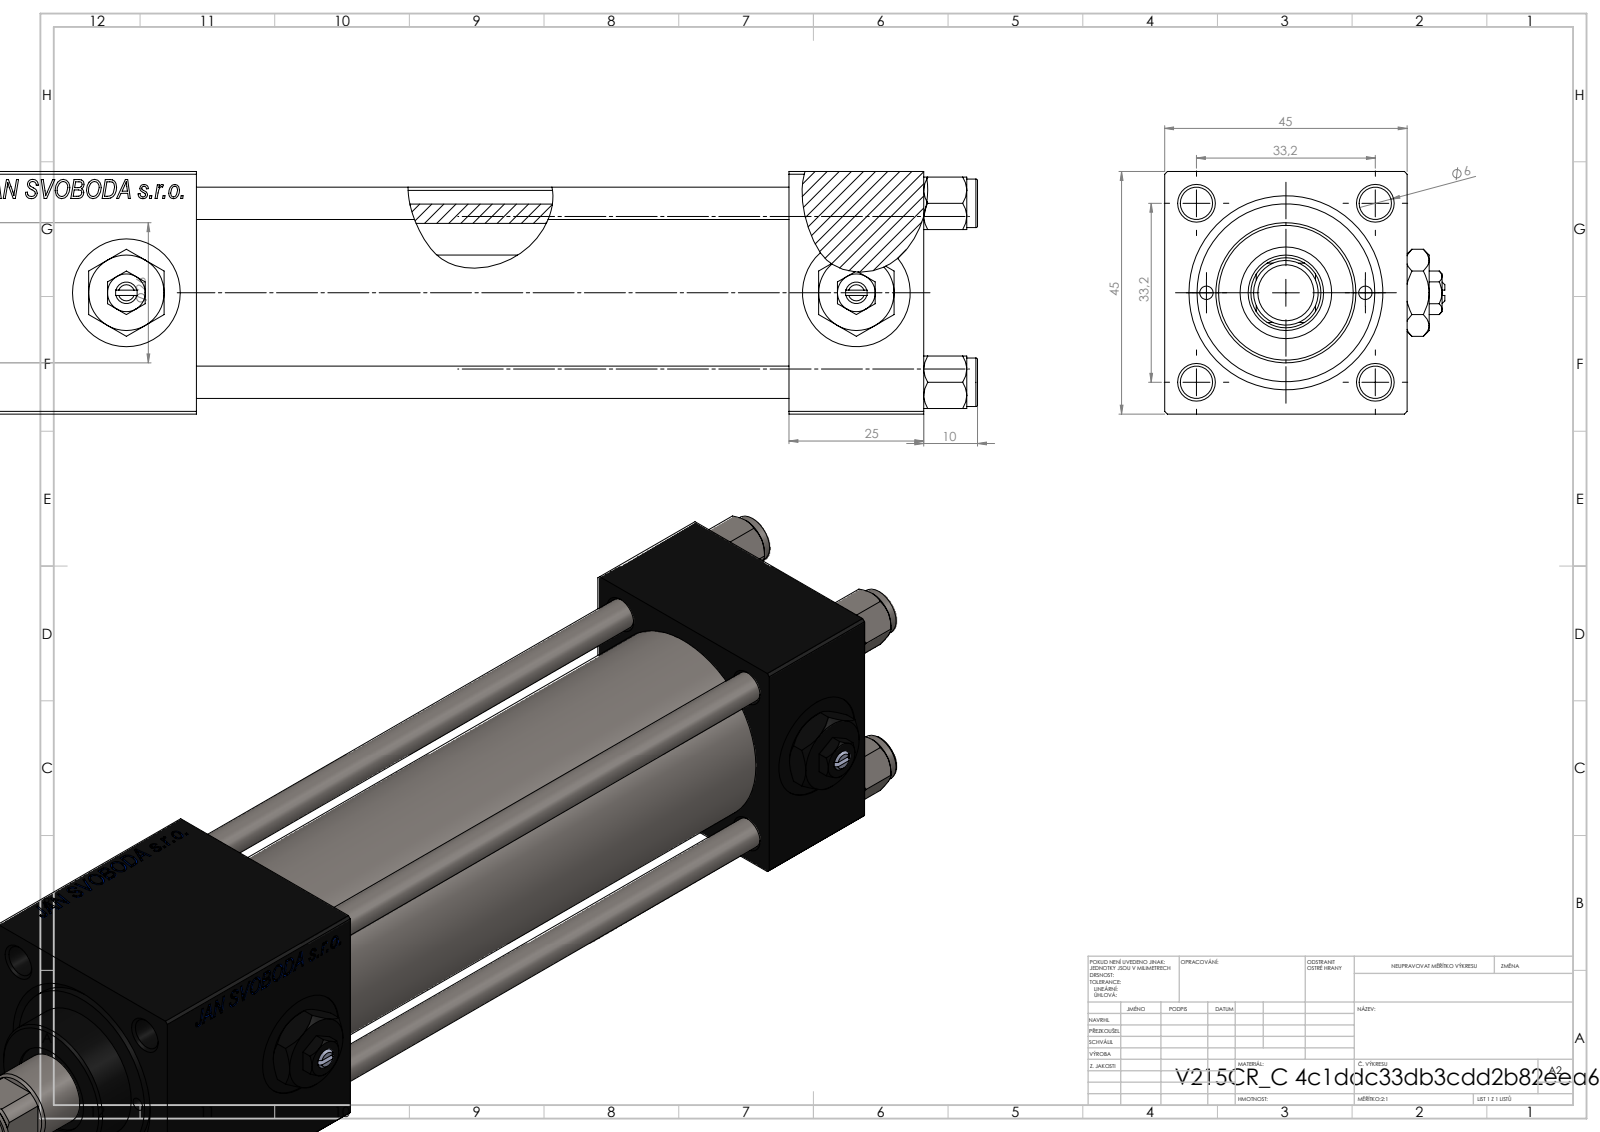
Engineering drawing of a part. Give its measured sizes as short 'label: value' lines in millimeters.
name: V215_VC_A; Zatka_pro_OIL_PORT; ROD_END_AH; V215CR_C_Body (+3 more)
written by: SolidWorks 2019 (CONFIG_CONTROL_DESIGN)
unit: mm
bodies: 14 solids, 1268 faces (578 planar, 106 cylindrical, 584 other)
size: 234 × 52 × 45
volume: 229 834 mm³; area: 90 211 mm²
holes: 4× ⌀6, 2× ⌀2.5, 2× ⌀7, 2× ⌀13.16, 2× ⌀20, 1× ⌀6.5, 1× ⌀14, 1× ⌀17, 1× ⌀24, 1× ⌀32, 1× ⌀33
bosses: 4× ⌀9, 1× ⌀38, 1× ⌀26, 1× ⌀12, 1× ⌀10
rounds: 1× R6.5
face distances: 45, 25, 183, 158, 135, 110, 48, 154.3, 129.3, 19.3
hole spacings: 16.7, 23.48, 33.2, 35.47, 14.75, 46.95, 29.5, 135.5
